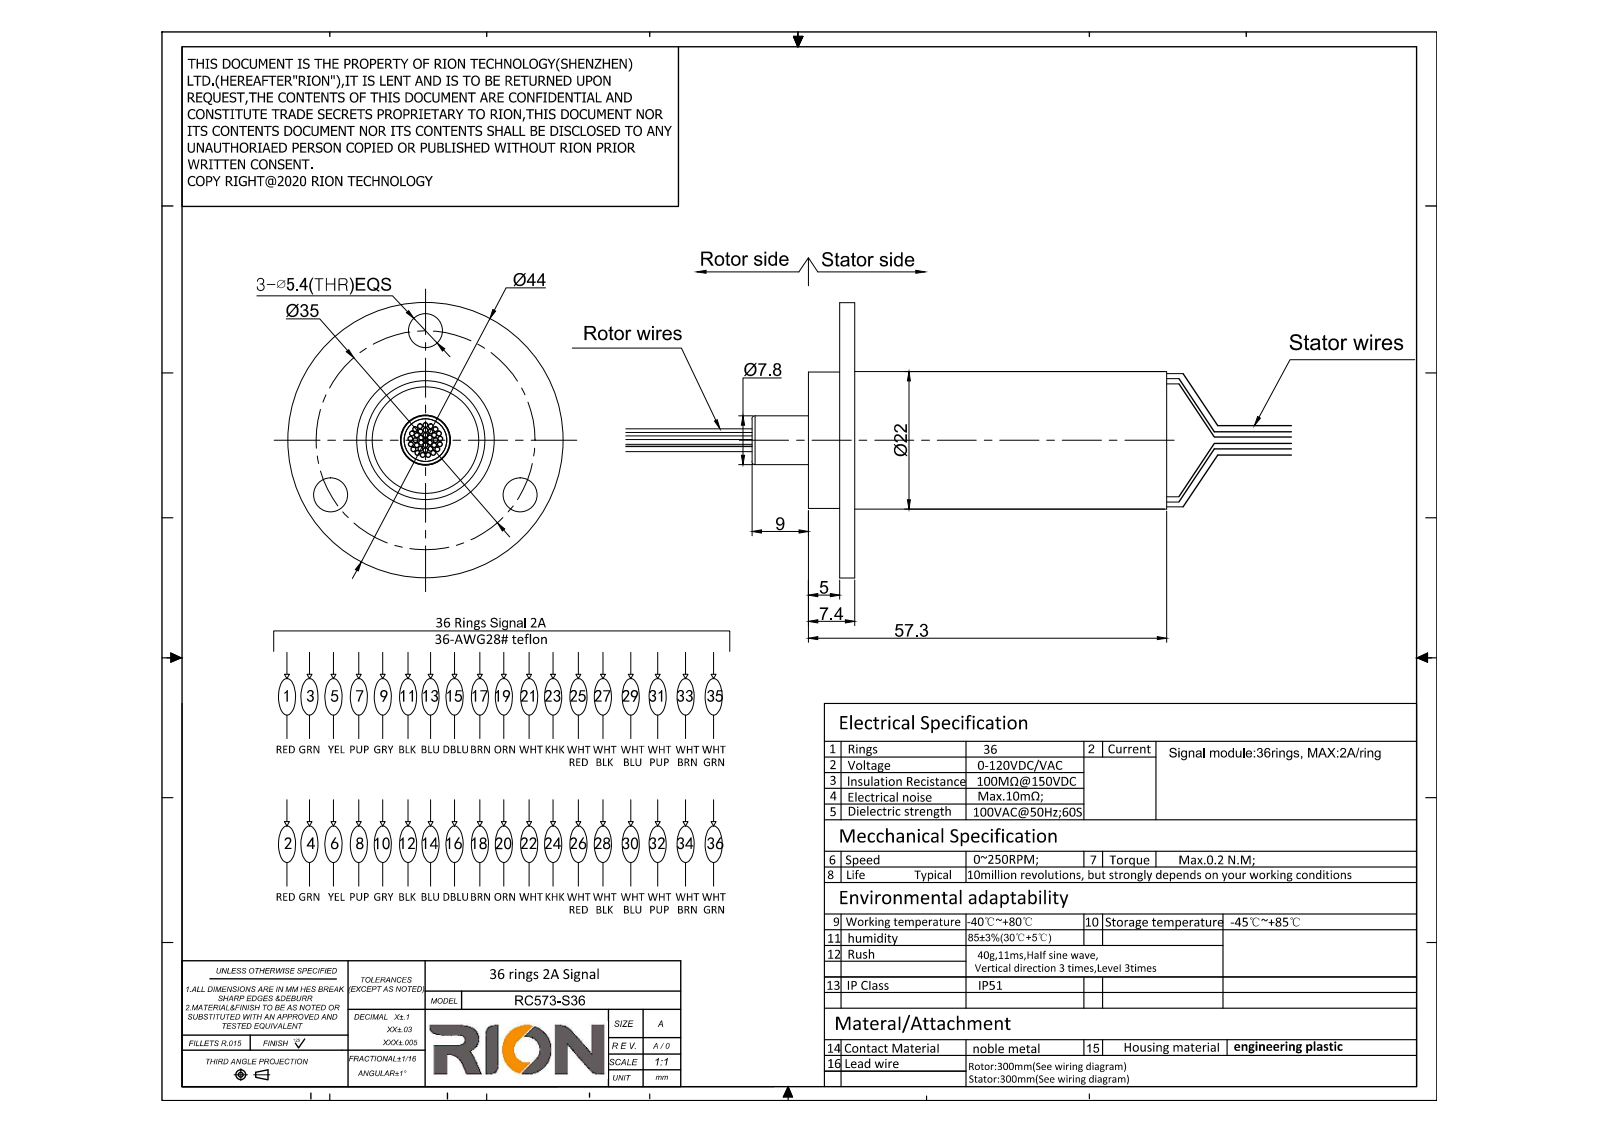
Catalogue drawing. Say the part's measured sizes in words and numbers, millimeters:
The part is named "MC573". Its 3-D file was written by "SolidWorks 2010 (CONFIG_CONTROL_DESIGN)". It is 1 solid with 260 faces: 88 planar, 168 cylindrical and 4 other. Overall it measures 84.3 by 44 by 44 millimeters. Its volume is 24 922 cubic millimeters and its surface area 9 539 square millimeters. Round holes: 3 of diameter 5.4, 1 of diameter 5.8, 1 of diameter 19. Round bosses or shafts: 72 of diameter 0.8, 1 of diameter 44, 1 of diameter 22, 1 of diameter 16, 1 of diameter 7.8. Partial cylindrical surfaces (rounded edges, fillets, slot ends): 1 of radius 9.45. The main face-to-face distances are 2.4, 52.3, 49.9, 5, 7.4, 57.3, 2, 3, 5.4, 55.3. The hole center spacings are 17.5, 30.31, 30.32.
